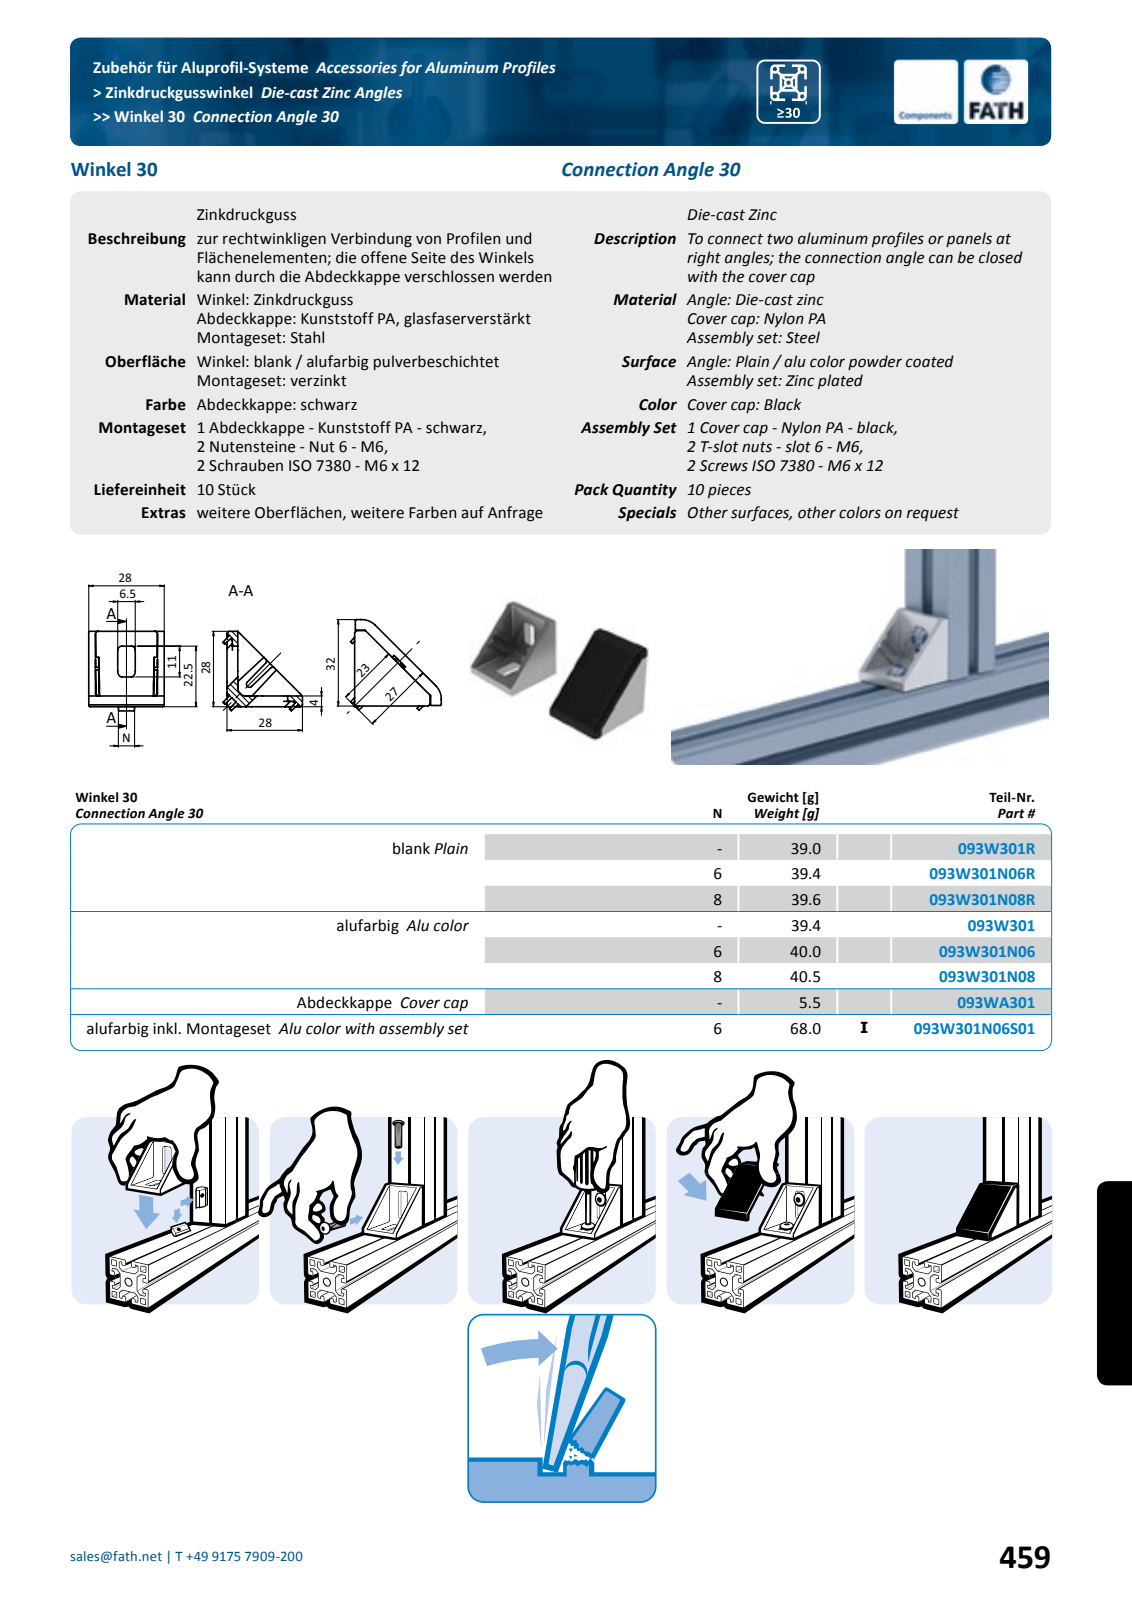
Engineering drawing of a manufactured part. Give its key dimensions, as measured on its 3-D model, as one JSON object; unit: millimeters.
{"part_name": "fath_093w301n08r", "step_written_by": "Spatial InterOp 3D (automotive_design)", "units": "millimeters", "bodies": {"solids": 1, "faces": 146, "planar": 107, "cylindrical": 37, "other": 2}, "overall_size": [38.6, 28, 22.57], "volume_mm3": 5993, "surface_area_mm2": 5138, "partial_cylinders_radius": [[1, 12], [0.5, 9], [1.5, 8], [1.13, 2], [3, 1]], "face_to_face_distances": [4, 1, 28, 24, 1.2, 3, 27, 19.98, 2, 6.5]}
